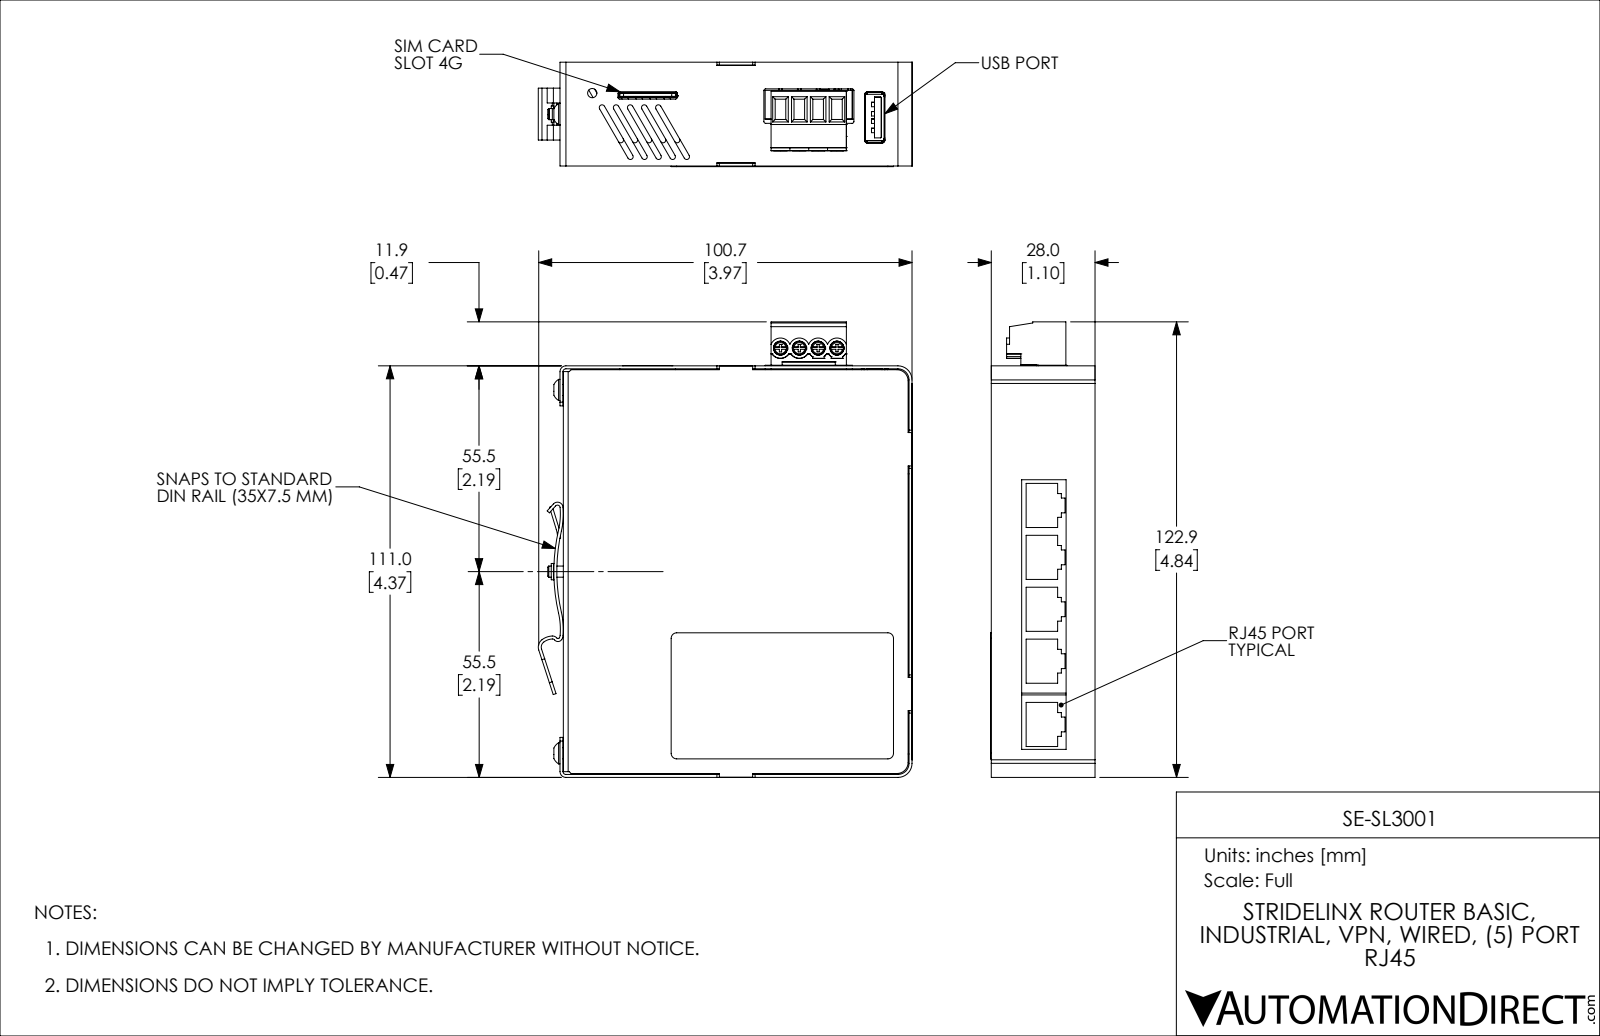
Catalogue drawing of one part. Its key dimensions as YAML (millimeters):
part_name: "SE-SL3001"
step_written_by: "SolidWorks 2019 (AUTOMOTIVE_DESIGN)"
units: millimeters
bodies: {solids: 73, faces: 2647, planar: 1962, cylindrical: 614, other: 71}
overall_size: [122.9, 100.9, 28.2]
volume: 45590
surface_area: 91550
round_holes:
  - {diameter: 2, count: 6}
  - {diameter: 2.5, count: 4}
  - {diameter: 3.8, count: 4}
  - {diameter: 3.5, count: 2}
  - {diameter: 0.2, count: 1}
  - {diameter: 3, count: 1}
  - {diameter: 3.3, count: 1}
  - {diameter: 4, count: 1}
  - {diameter: 4.4, count: 1}
  - {diameter: 5.4, count: 1}
  - {diameter: 5.4, count: 1}
round_bosses_or_shafts:
  - {diameter: 0.7, count: 39}
  - {diameter: 5.7, count: 4}
  - {diameter: 3.6, count: 4}
  - {diameter: 3.1, count: 4}
  - {diameter: 3, count: 3}
  - {diameter: 5.1, count: 1}
partial_cylinders:
  - {radius: 0.1, count: 91}
  - {radius: 0.2, count: 38}
  - {radius: 0.2, count: 33}
  - {radius: 0.8, count: 25}
  - {radius: 0.3, count: 24}
  - {radius: 1, count: 19}
  - {radius: 0.5, count: 14}
  - {radius: 0.6, count: 8}
face_to_face_distances: [0.8, 27.2, 28, 26.4, 93.3, 110.2, 94.1, 1, 28.2, 27.4]
hole_center_spacings: [5.1, 2.5, 8, 7.6, 9.2, 10.2, 41, 43.5]
